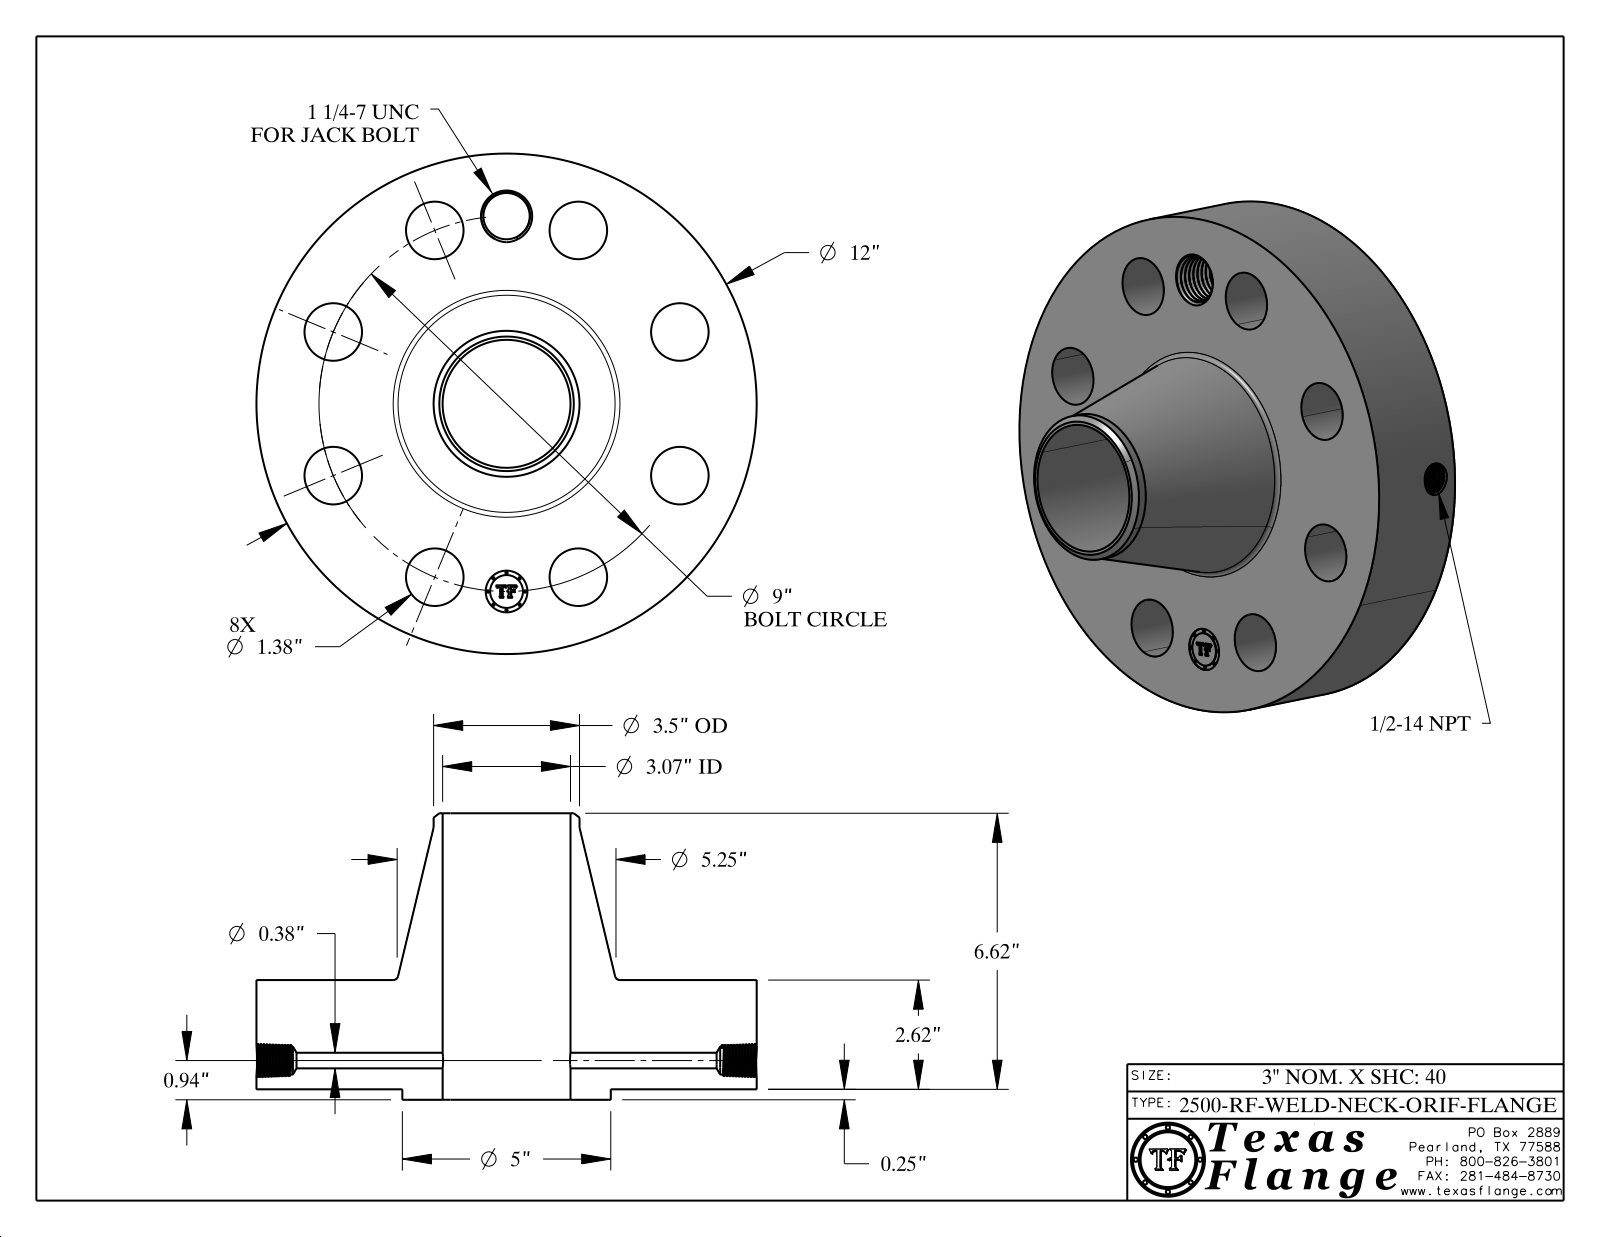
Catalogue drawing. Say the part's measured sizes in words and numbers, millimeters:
The part is named "2500-RF-WELD-NECK". Its 3-D file was written by "CATIA V5 STEP AP214 (AUTOMOTIVE_DESIGN)". It is 1 solid with 790 faces: 369 planar, 100 cylindrical and 321 other. Overall it measures 304.8 by 304.8 by 174.5 millimeters. Its volume is 4 484 000 cubic millimeters and its surface area 332 800 square millimeters. Round holes: 8 of diameter 35.1, 1 of diameter 9.5, 1 of diameter 17.1, 1 of diameter 25.4, 1 of diameter 28.2, 1 of diameter 77.9. Round bosses or shafts: 8 of diameter 1.5, 1 of diameter 304.8, 1 of diameter 127, 1 of diameter 88.9, 1 of diameter 20. The main face-to-face distances are 66.5, 6.4, 72.9, 174.5, 168.1, 101.6, 72.5, 66.2, 0.4, 102. The hole center spacings are 114.3, 87.5, 161.6, 211.2, 228.6, 44.6, 127, 190.1.
